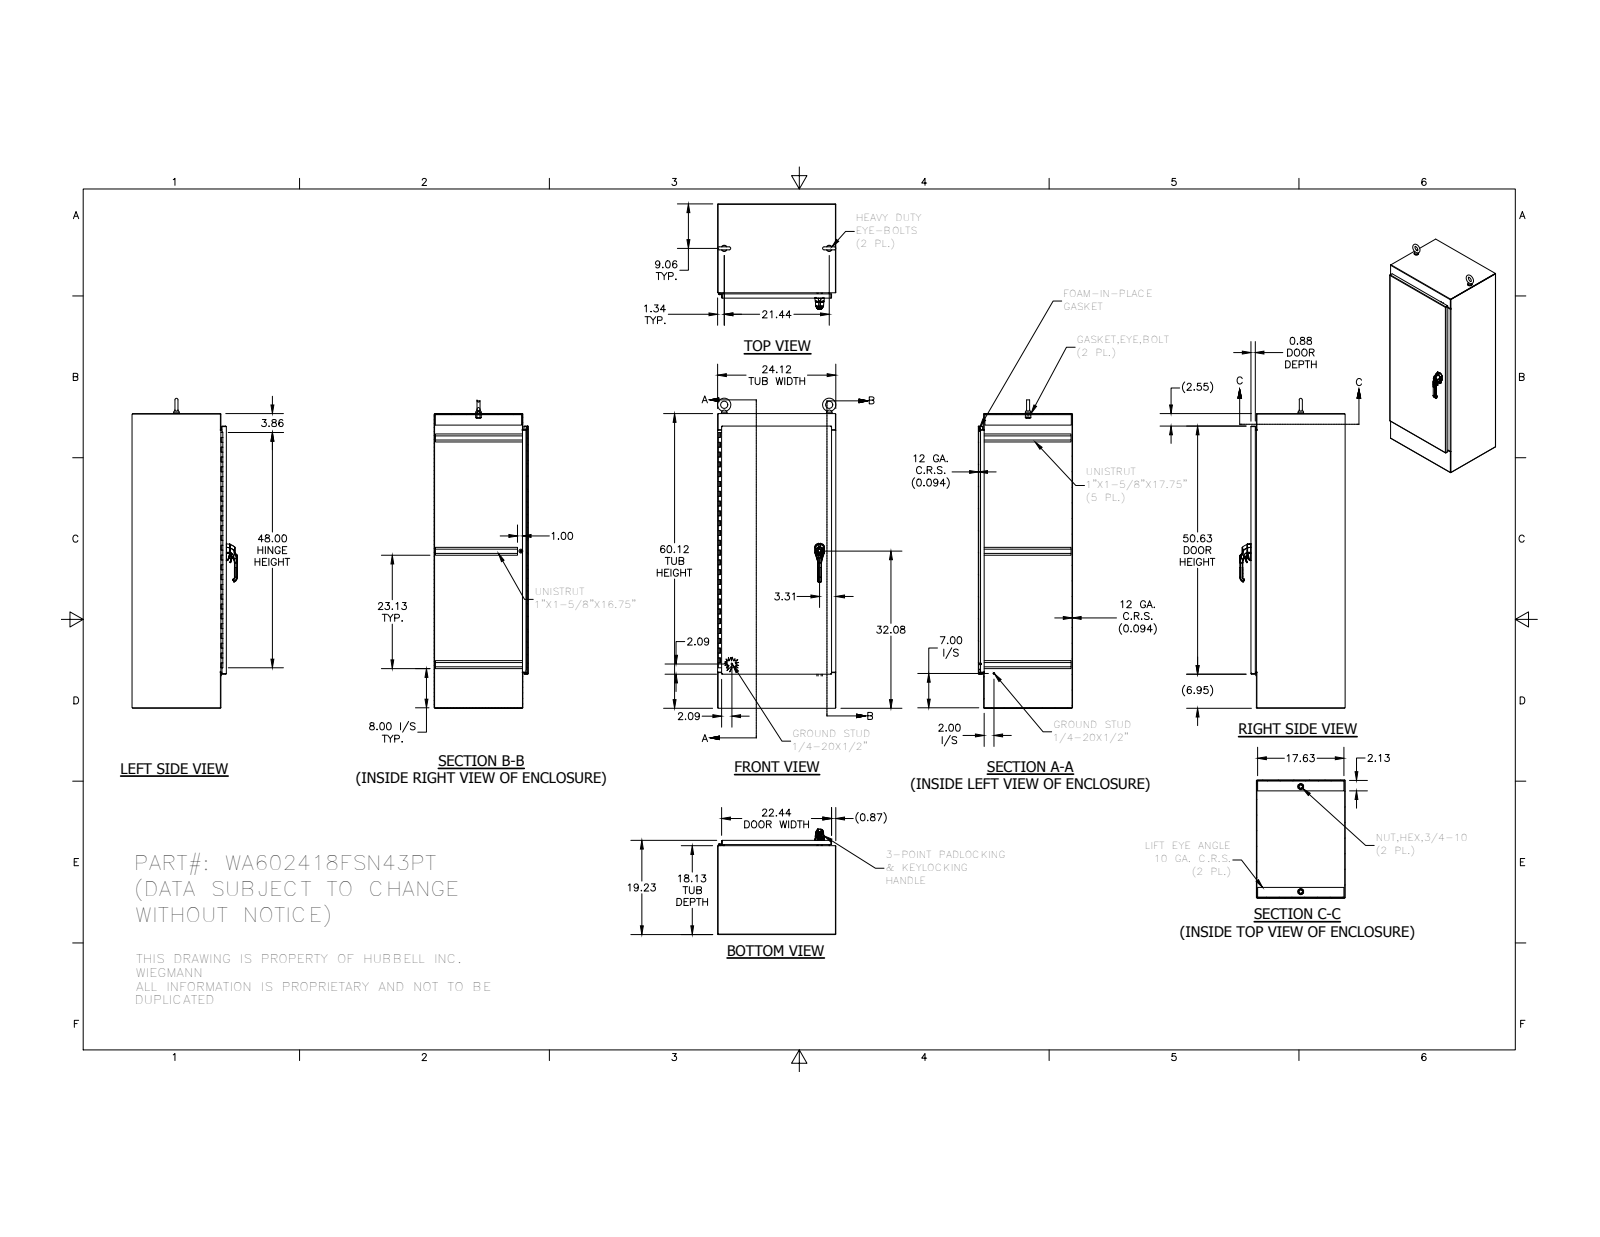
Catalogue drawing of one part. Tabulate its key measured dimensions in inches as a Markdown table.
| quantity | value |
| --- | --- |
| part name | 31215; 30624; WA602418FSN43PT; 3021WIE (+8 more) |
| STEP written by | SolidWorks 2014 (AUTOMOTIVE_DESIGN) |
| units | inches |
| bodies | 50 solids, 1630 faces (690 planar, 620 cylindrical, 320 other) |
| overall size | 63.248 × 24.125 × 19.227 |
| volume | 705.7 in³ |
| surface area | 14 546 in² |
| round holes (diameter × count) | 0.277 × 8, 0.375 × 8, 0.2 × 4, 0.28 × 3, 0.241 × 2, 0.25 × 2, 0.252 × 2, 0.4 × 2, 0.407 × 2, 0.45 × 2, 0.642 × 2, 0.813 × 2 |
| round bosses / shafts (diameter × count) | 1.25 × 2, 1.12 × 2, 1 × 2, 0.75 × 2, 0.563 × 2, 0.527 × 2, 0.5 × 2, 0.375 × 2 |
| partial cylindrical surfaces (radius × count) | 0.031 × 17, 0.01 × 16, 0.125 × 16, 0.125 × 15, 0.05 × 14, 0.019 × 12, 0.053 × 12, 0.086 × 12 |
| main face-to-face distances | 0.094, 19.133, 24.031, 19.039, 23.938, 19.227, 24.125, 60.031, 18.031, 1.102 |
| hole center spacings | 5.333, 16, 10.667, 21.333, 0.762, 0.764, 1.195, 1.271 |
